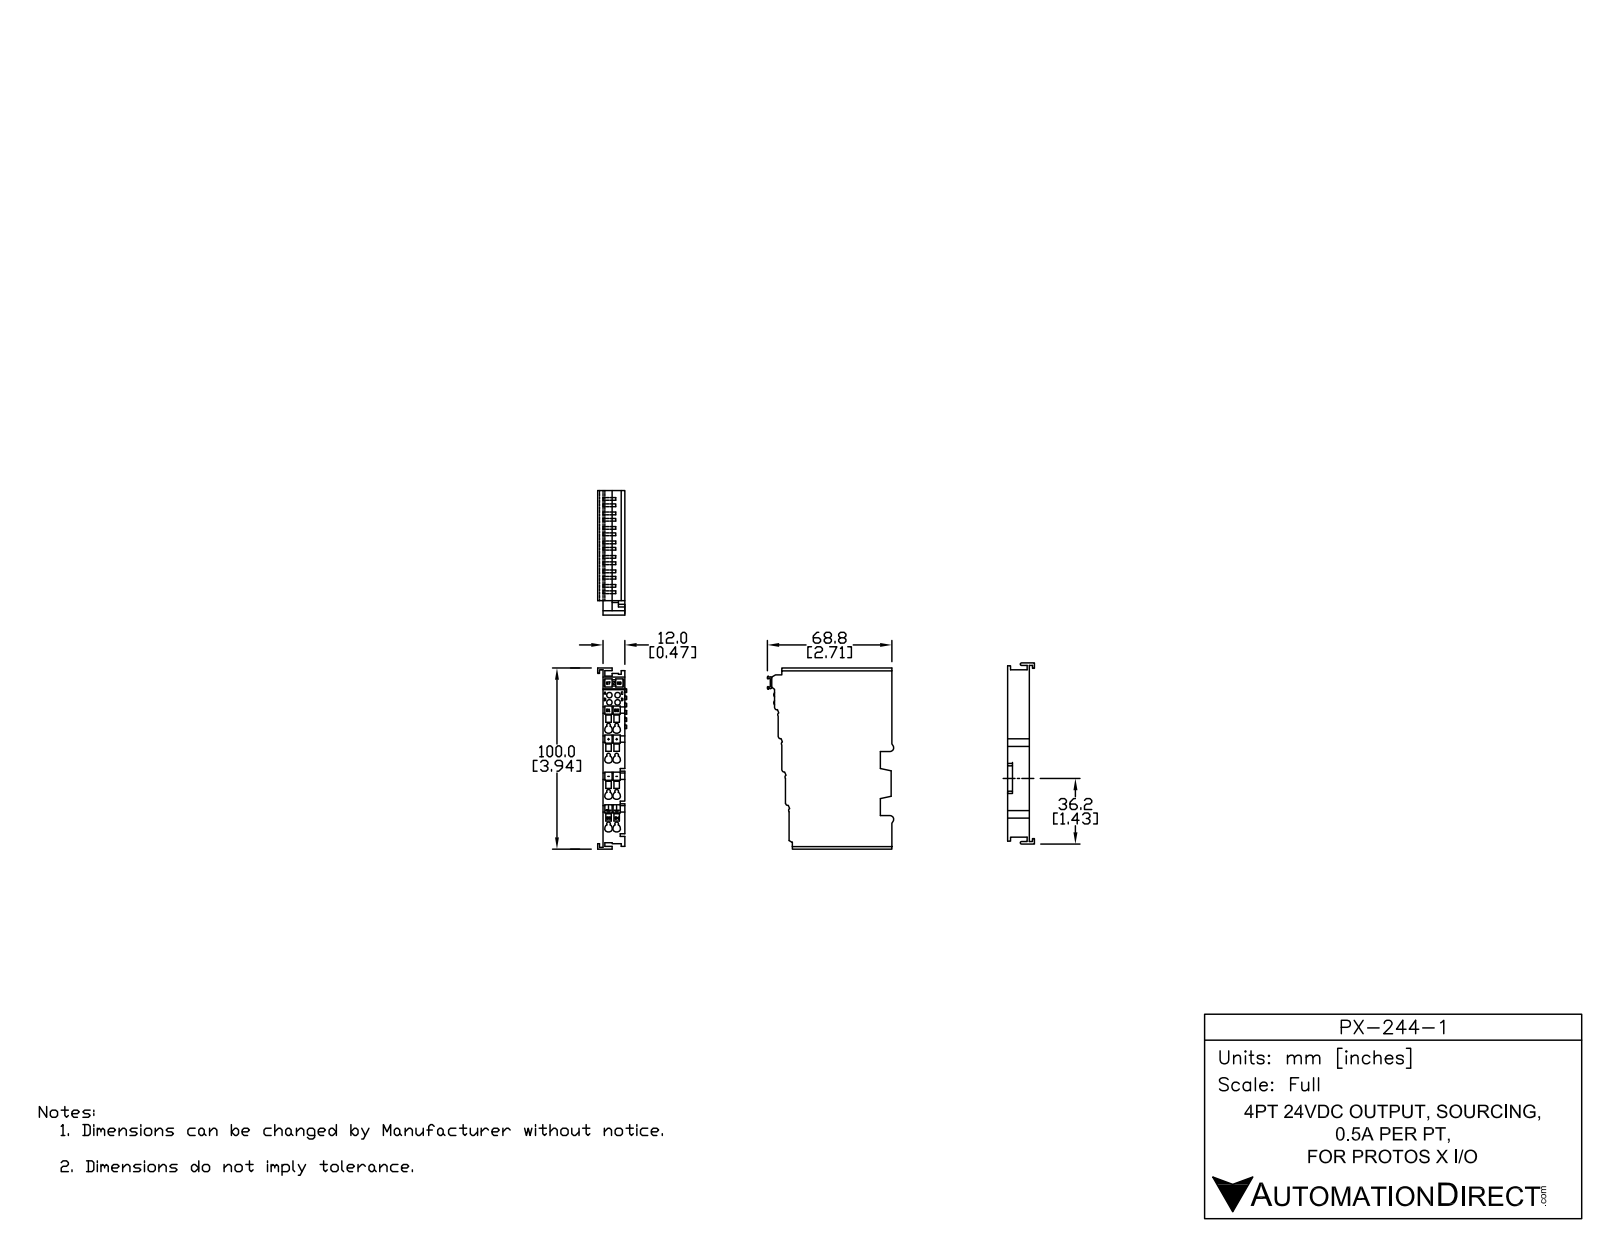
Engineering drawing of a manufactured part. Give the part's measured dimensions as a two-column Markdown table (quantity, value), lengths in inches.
| quantity | value |
| --- | --- |
| part name | PX-244-1 |
| STEP written by | SolidWorks 2014 (AUTOMOTIVE_DESIGN) |
| units | inches |
| bodies | 28 solids, 1367 faces (963 planar, 344 cylindrical, 60 other) |
| overall size | 3.947 × 2.806 × 0.596 |
| volume | 3.564 in³ |
| surface area | 52.52 in² |
| round holes (diameter × count) | 0.157 × 8, 0.138 × 4 |
| partial cylindrical surfaces (radius × count) | 0.012 × 46, 0.01 × 35, 0.015 × 12, 0.005 × 10, 0.039 × 9, 0.016 × 8, 0.007 × 4, 0.041 × 4 |
| main face-to-face distances | 0.472, 0.039, 0.079, 0.394, 0.073, 0.433, 0.343, 0.157, 0.124, 0.048 |
| hole center spacings | 0.177, 0.197, 0.724, 0.751, 0.25, 0.63, 0.66, 0.804 |
